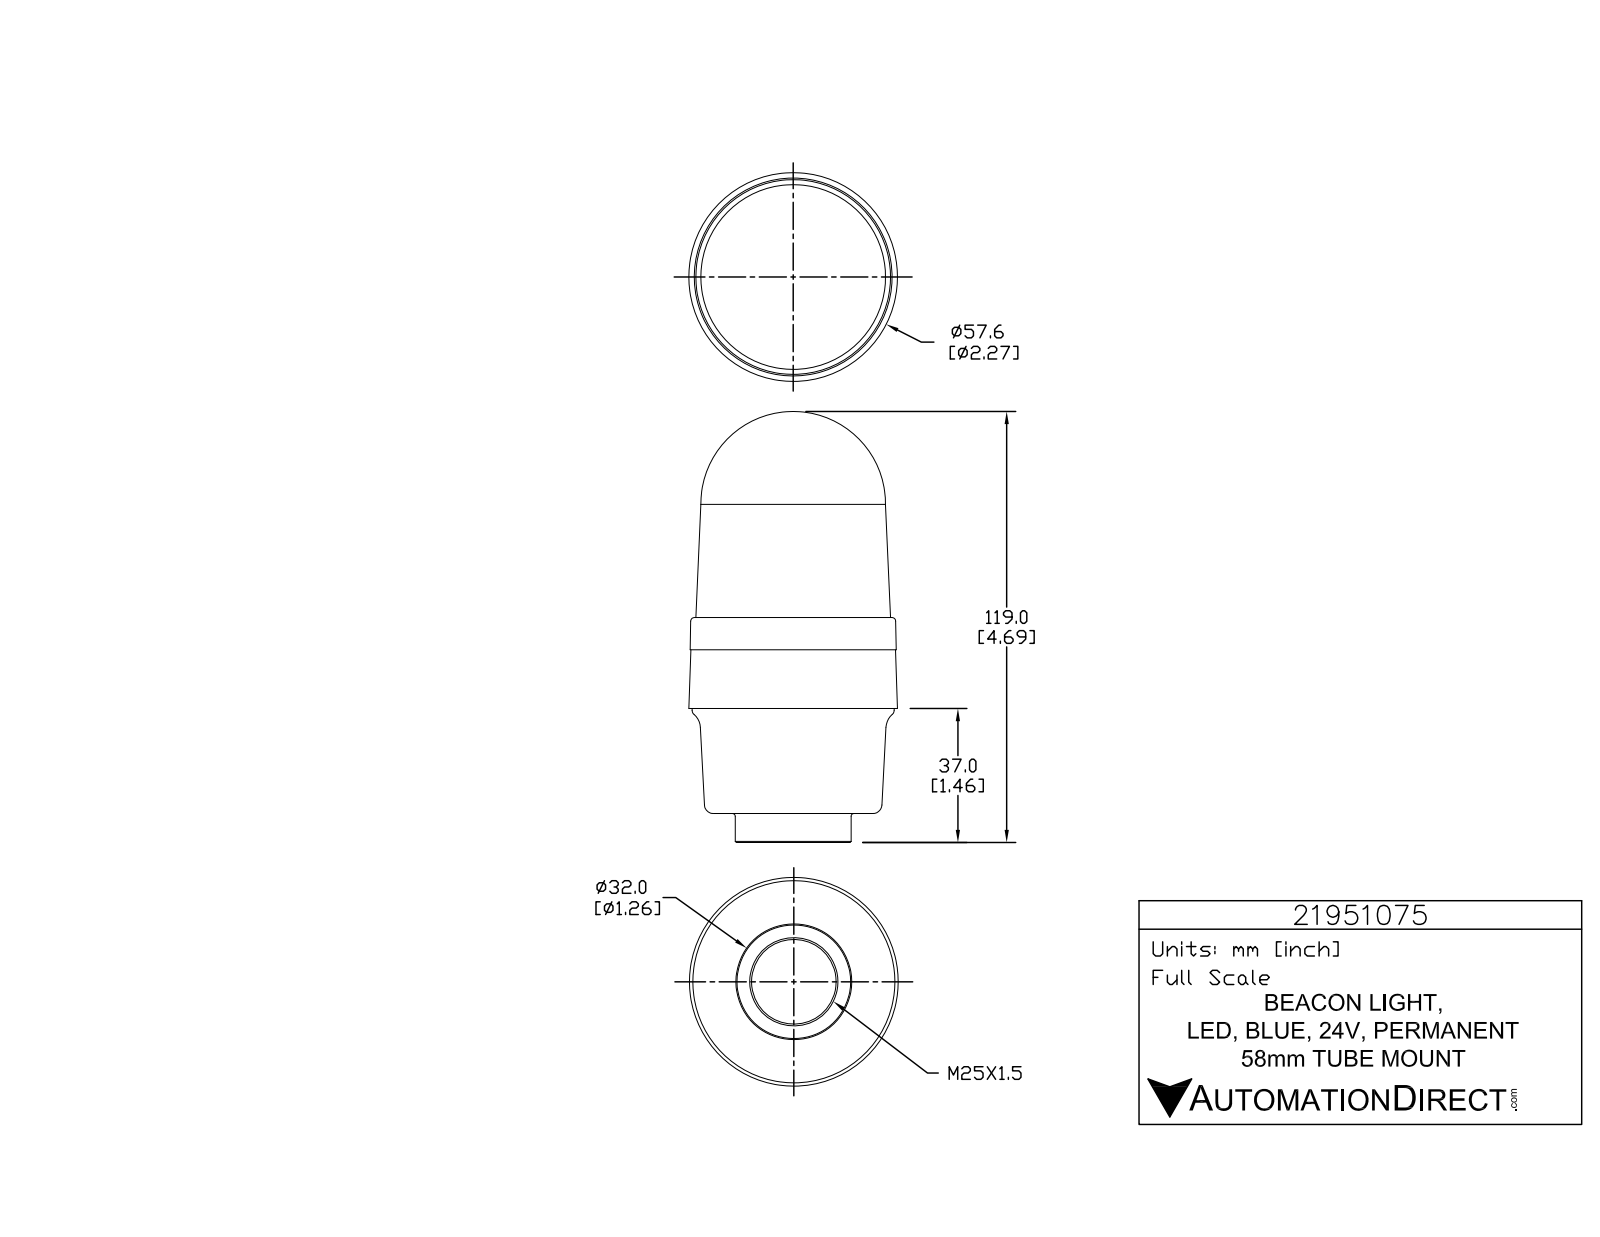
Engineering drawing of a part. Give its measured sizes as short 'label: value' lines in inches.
name: 21951075
written by: SolidWorks 2015 (AUTOMOTIVE_DESIGN)
unit: in
bodies: 1 solid, 791 faces (525 planar, 168 cylindrical, 98 other)
size: 4.685 × 2.269 × 2.269
volume: 13.89 in³; area: 34.06 in²
holes: 3× ⌀0.039, 1× ⌀0.92
bosses: 3× ⌀0.226, 3× ⌀0.056, 1× ⌀2.197, 1× ⌀1.26
rounds: 6× R0.008, 6× R0.008, 6× R0.008, 6× R0.131, 3× R0.004, 3× R0.005, 3× R0.008, 3× R0.008
face distances: 0.315, 1.142, 1.457, 0.988, 2.13, 2.445, 0.35, 0.638, 1.78, 2.094
